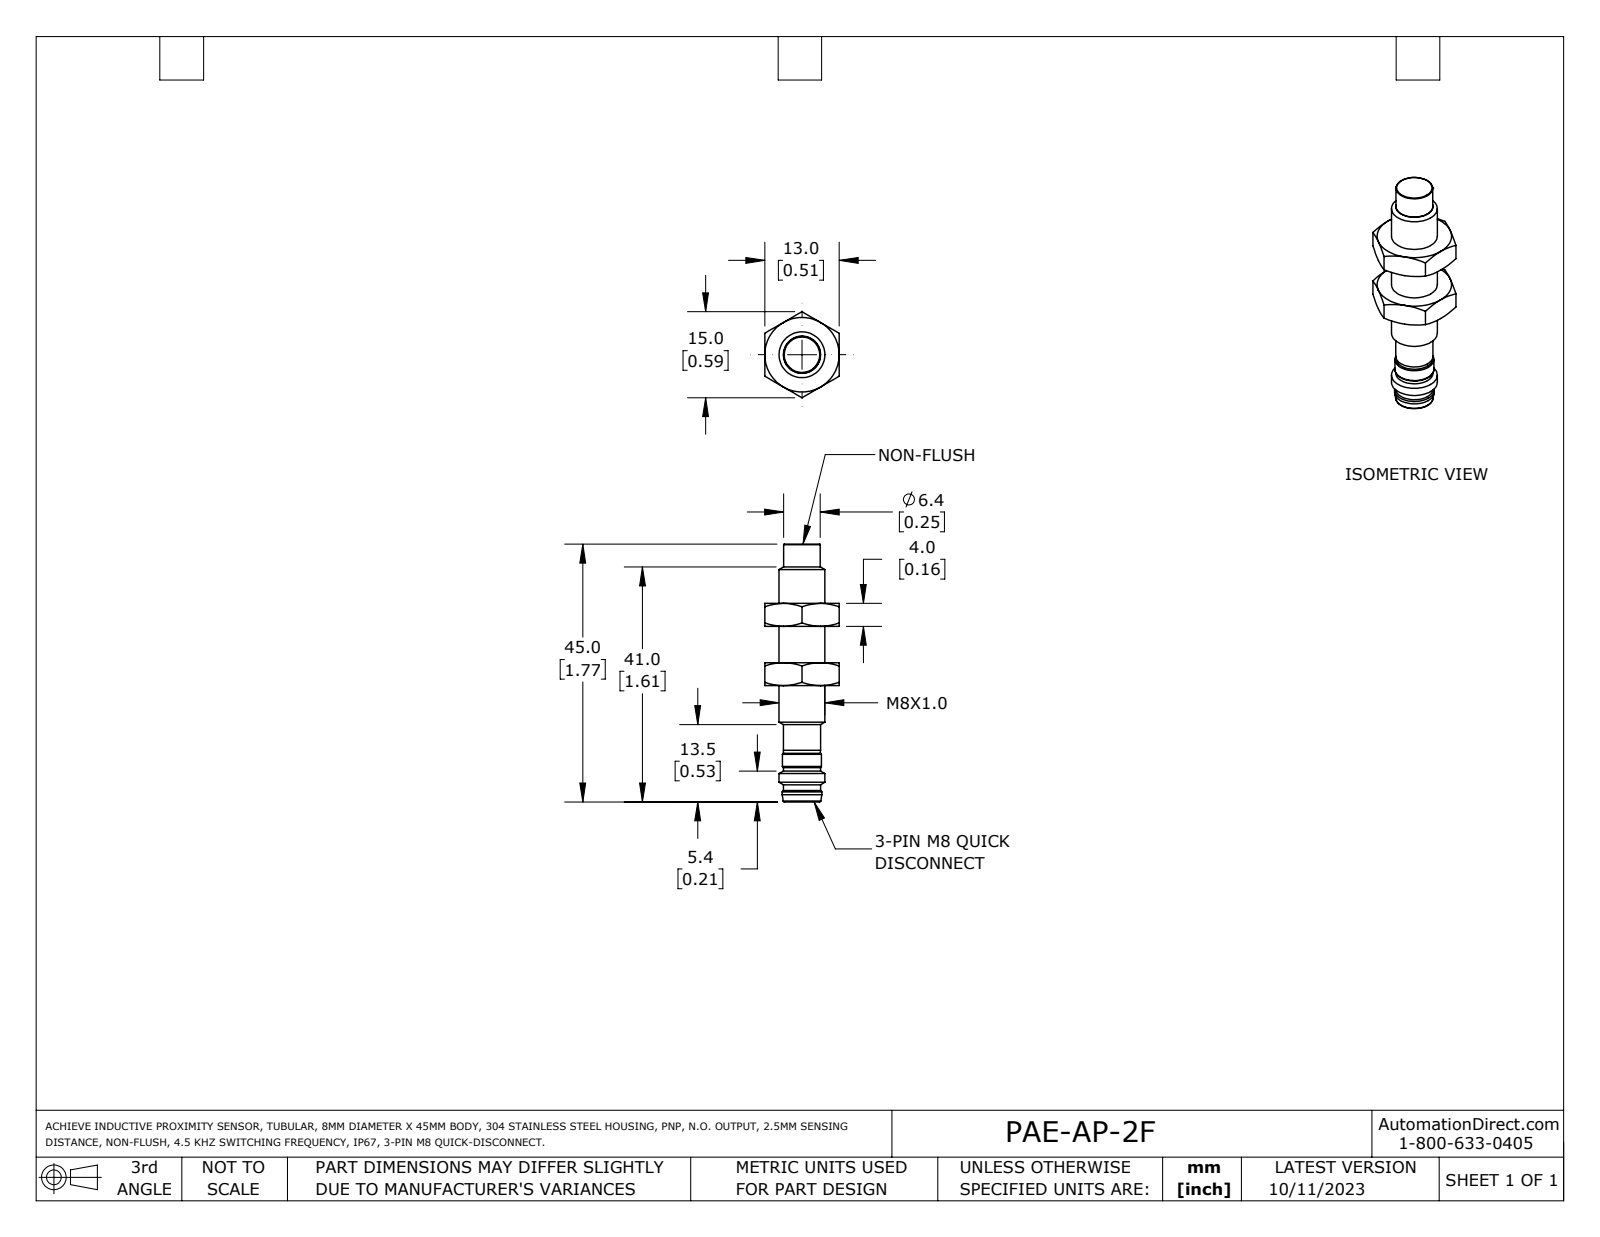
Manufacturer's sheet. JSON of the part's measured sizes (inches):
{"part_name": "PAE-AP-2F", "step_written_by": "SolidWorks 2023 (AUTOMOTIVE_DESIGN)", "units": "inches", "bodies": {"solids": 3, "faces": 76, "planar": 26, "cylindrical": 15, "other": 35}, "overall_size": [1.772, 0.591, 0.512], "volume_in3": 0.161, "surface_area_in2": 3.438, "round_holes": [[0.228, 1], [0.315, 1]], "round_bosses_or_shafts": [[0.039, 3], [0.272, 1], [0.268, 1], [0.256, 1], [0.254, 1], [0.252, 1]], "face_to_face_distances": [0.407, 0.157, 0.512, 0.565, 0.25, 0.815, 0.972, 0.602, 1.01, 0.76]}
